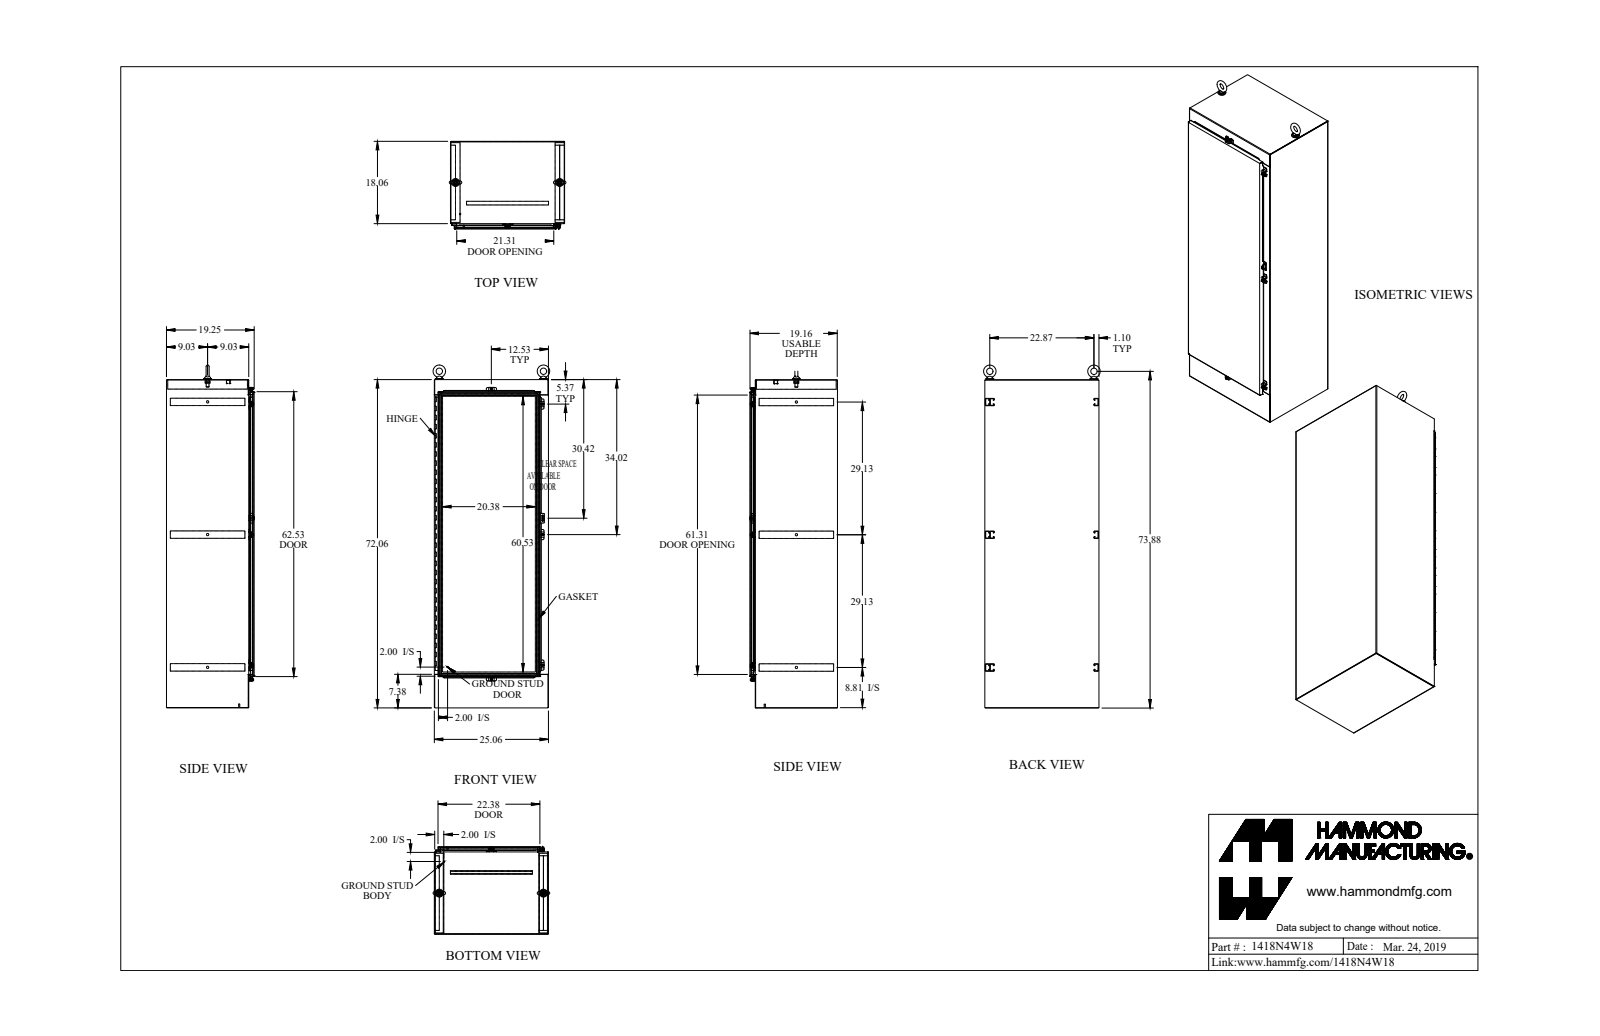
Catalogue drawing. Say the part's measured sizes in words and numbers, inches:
The part is named "1418N4W18_Default". Its 3-D file was written by "SolidWorks 2019 (CONFIG_CONTROL_DESIGN)". It is 52 solids with 2017 faces: 1074 planar, 847 cylindrical and 96 other. Overall it measures 75.713 by 26.118 by 19.31 inches. Its volume is 822 cubic inches and its surface area 17 437 square inches. Round holes: 10 of diameter 0.304, 5 of diameter 0.213, 5 of diameter 0.265, 5 of diameter 0.375, 3 of diameter 0.5, 2 of diameter 0.527, 2 of diameter 0.625, 2 of diameter 0.687, 2 of diameter 0.75, 1 of diameter 0.11, 1 of diameter 0.125. Round bosses or shafts: 5 of diameter 0.5, 5 of diameter 0.39, 5 of diameter 0.244, 2 of diameter 1.75, 2 of diameter 1.5, 2 of diameter 1.25, 2 of diameter 0.738, 2 of diameter 0.281. Partial cylindrical surfaces (rounded edges, fillets, slot ends): 60 of radius 0.043, 54 of radius 0.138, 45 of radius 0.048, 45 of radius 0.143, 26 of radius 0.25, 10 of radius 0.06, 10 of radius 0.141, 8 of radius 0.125. The main face-to-face distances are 0.095, 19.152, 24.965, 24.87, 19.057, 19.247, 25.06, 1.187, 17.965, 71.965. The hole center spacings are 6, 12, 18, 24, 30, 36, 42, 29.13.
